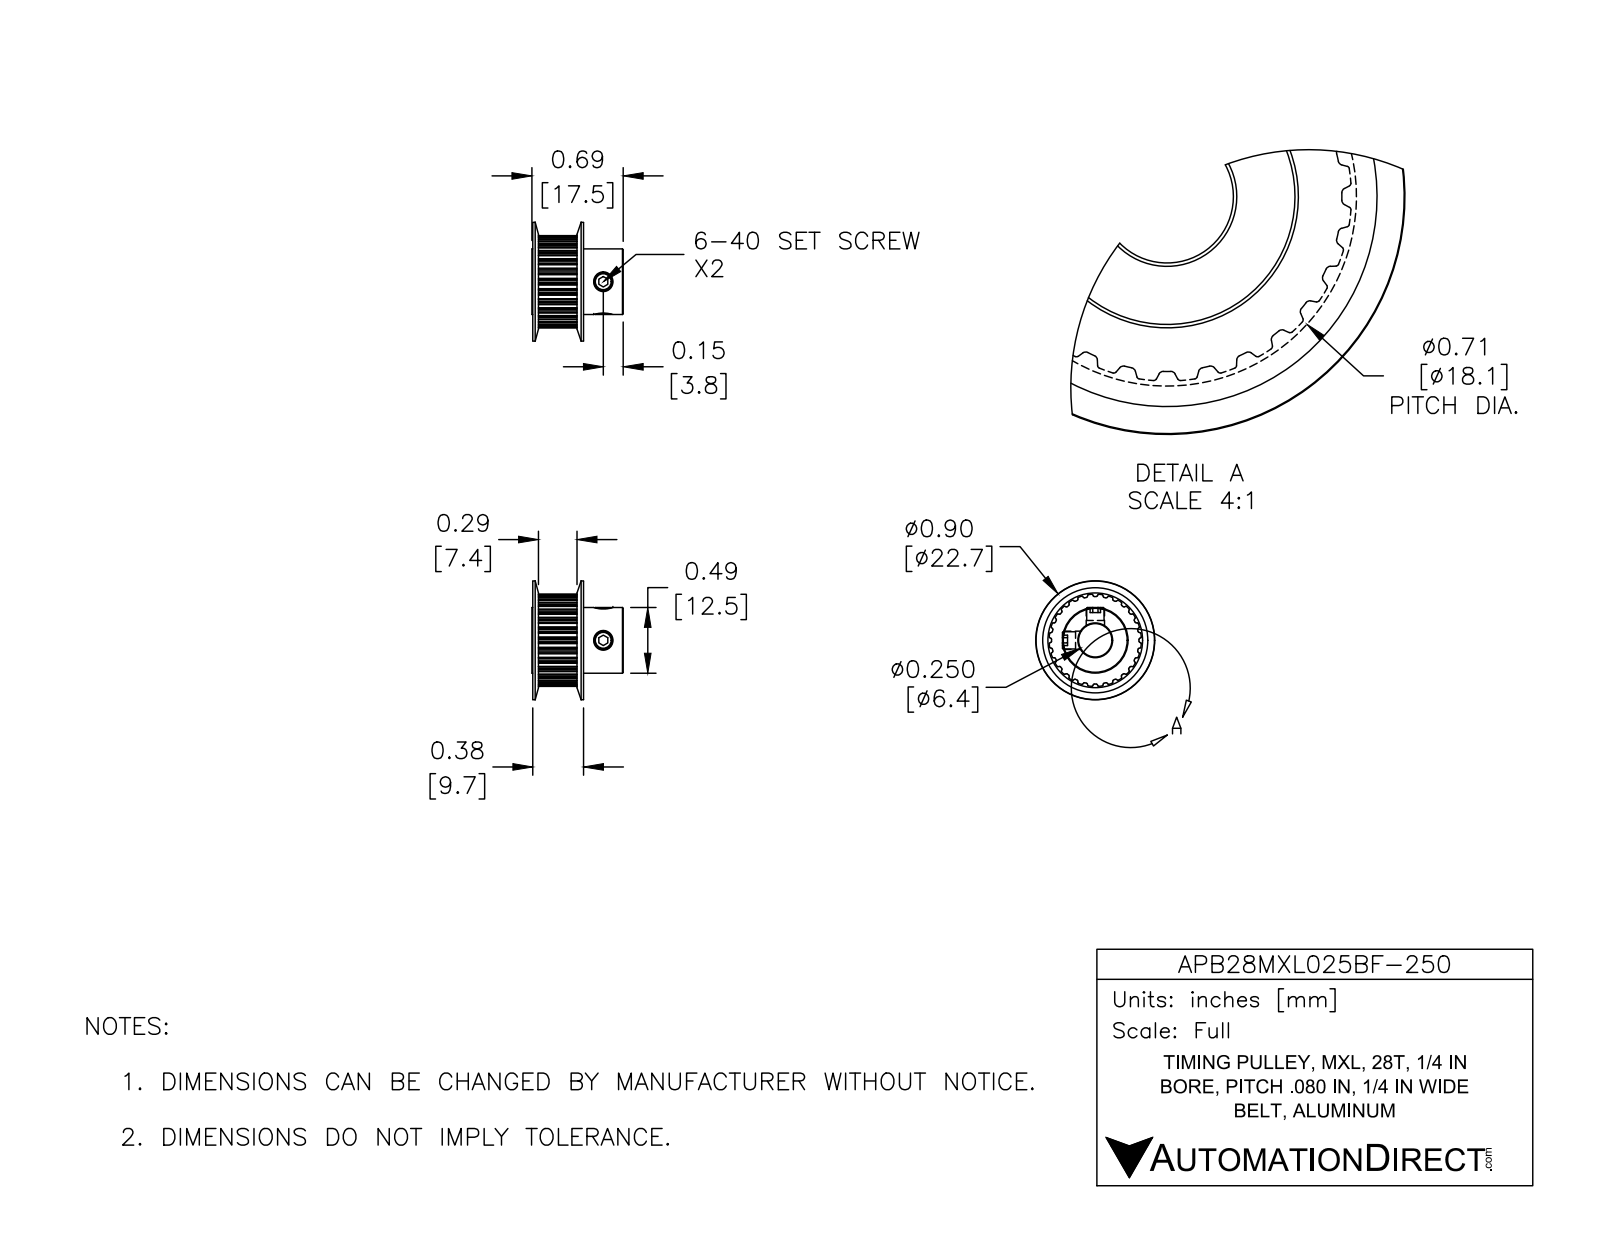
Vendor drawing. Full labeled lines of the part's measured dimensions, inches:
Part name (STEP PRODUCT): APB28MXL025BF-250
STEP written by: SolidWorks 2016 (AUTOMOTIVE_DESIGN)
Units: inches
Bodies: 3 solids, 309 faces (80 planar, 203 cylindrical, 26 other)
Overall size (bounding box): 0.895 × 0.895 × 0.688
Volume: 0.166 in³ · Surface area: 3.852 in²
Round holes (diameter × count): ⌀0.138 ×2, ⌀0.25 ×1
Round bosses / shafts (diameter × count): ⌀0.13 ×2, ⌀0.494 ×1
Partial cylindrical surfaces — rounded edges, fillets, slot ends (radius × count): R0.005 ×56, R0.009 ×56, R0.329 ×1, R0.347 ×1
Main face-to-face distances: 0.346, 0.025, 0.37, 0.687, 0.663, 0.317, 0.287, 0.34, 0.315, 0.031
